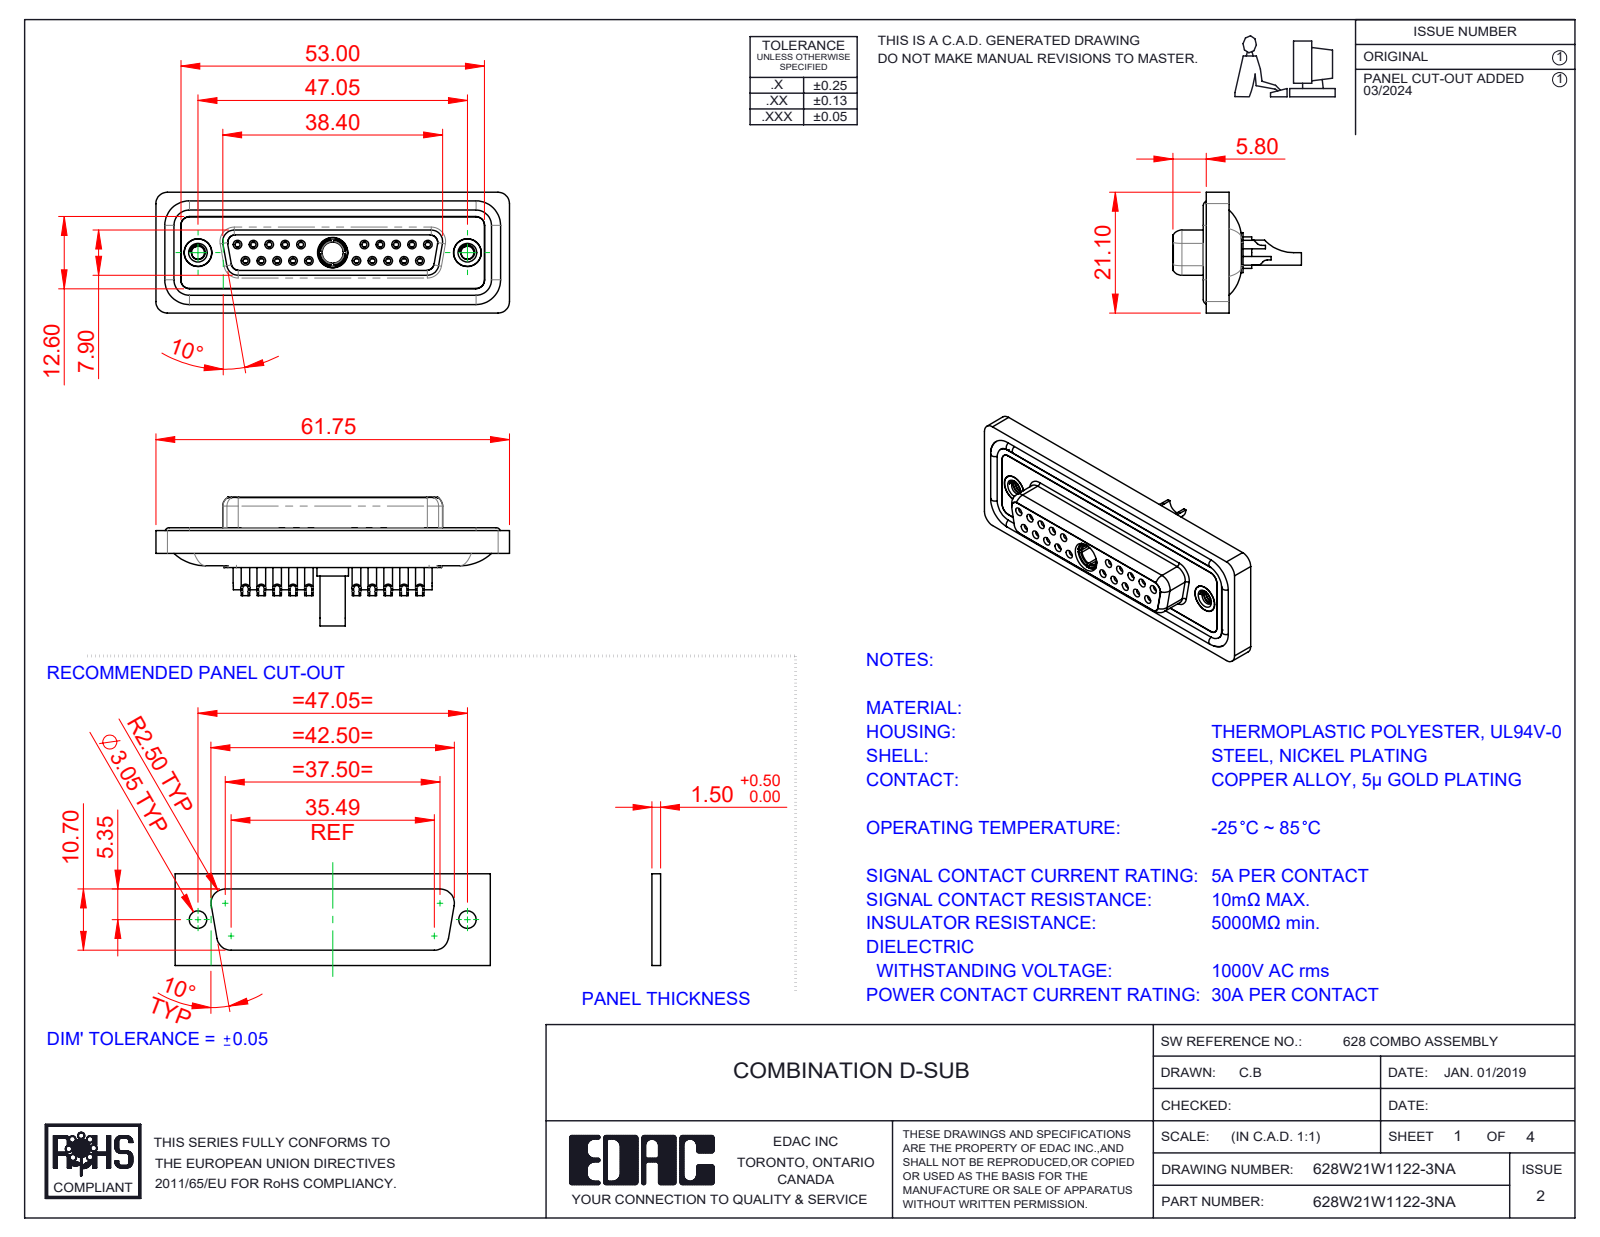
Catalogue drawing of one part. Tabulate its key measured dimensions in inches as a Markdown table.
| quantity | value |
| --- | --- |
| part name | 628Combo Threaded Rivet_A; 628Combo Waterproof Housing_25 Contacts; 628Combo Shell Front_25 Contacts; 628Combo Housing_21W1 (+5 more) |
| STEP written by | SolidWorks 2023 (CONFIG_CONTROL_DESIGN) |
| units | inches |
| bodies | 29 solids, 1564 faces (477 planar, 636 cylindrical, 451 other) |
| overall size | 2.431 × 0.884 × 0.831 |
| volume | 0.515 in³ |
| surface area | 22.19 in² |
| round holes (diameter × count) | 0.035 × 20, 0.039 × 20, 0.043 × 20, 0.059 × 20, 0.079 × 20, 0.063 × 10, 0.067 × 10, 0.191 × 3, 0.089 × 2, 0.157 × 2, 0.159 × 2, 0.197 × 2 |
| round bosses / shafts (diameter × count) | 0.087 × 20, 0.063 × 14, 0.195 × 2, 0.189 × 2, 0.217 × 1, 0.205 × 1, 0.195 × 1, 0.187 × 1 |
| partial cylindrical surfaces (radius × count) | 0.059 × 22, 0.079 × 18, 0.053 × 8, 0.063 × 8, 0.039 × 6, 0.01 × 4, 0.02 × 4, 0.024 × 4 |
| main face-to-face distances | 0.016, 0.071, 0.293, 0.222, 0.26, 0.02, 0.063, 0.278, 0.114, 0.043 |
| hole center spacings | 0.124, 0.109, 0.218, 0.198, 0.327, 0.294, 0.654, 0.763 |
